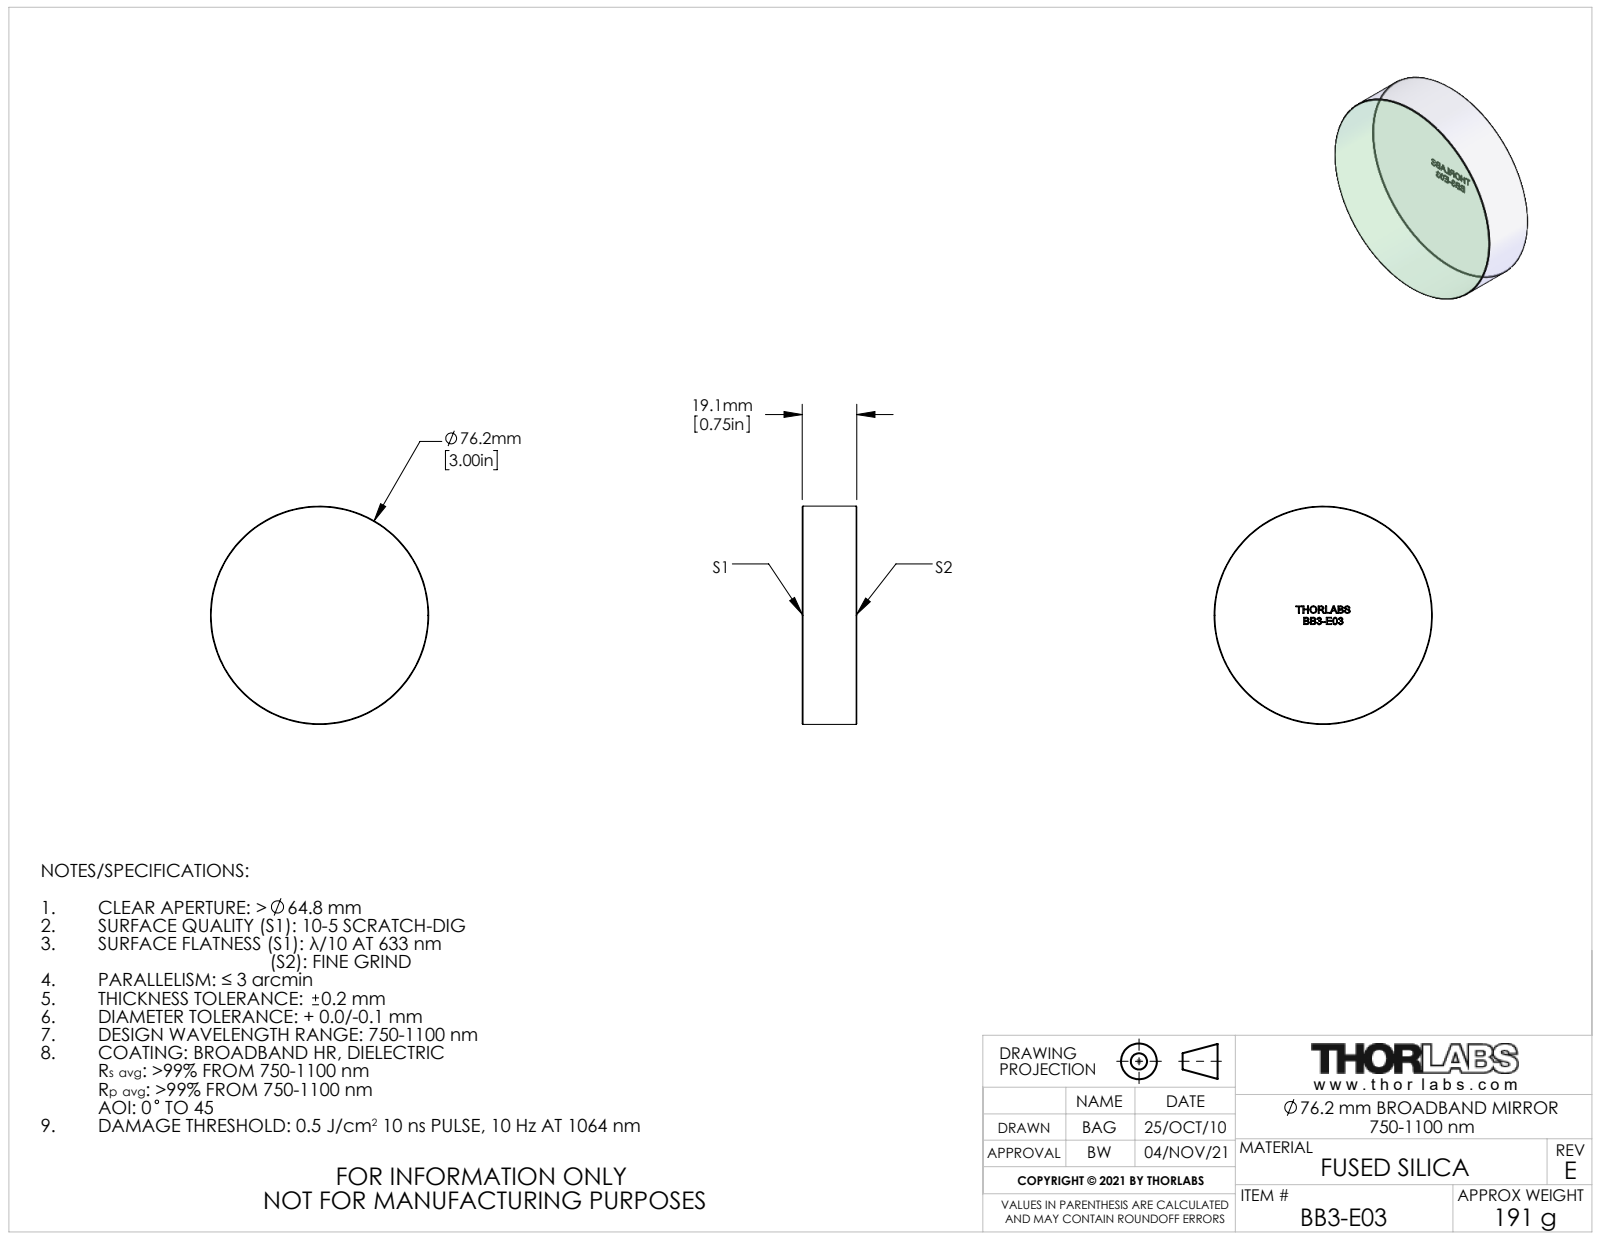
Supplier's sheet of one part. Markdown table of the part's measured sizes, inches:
| quantity | value |
| --- | --- |
| part name | 18643-E0W |
| STEP written by | SolidWorks 2016 (CONFIG_CONTROL_DESIGN) |
| units | inches |
| bodies | 1 solid, 232 faces (126 planar, 2 cylindrical, 104 other) |
| overall size | 3 × 3 × 0.75 |
| volume | 5.301 in³ |
| surface area | 21.1 in² |
| round bosses / shafts (diameter × count) | 3 × 1 |
| main face-to-face distances | 0.75, 0.75, 0.101, 0.156, 0.089, 0.014, 0.015, 0.046, 0.043, 0.198 |
